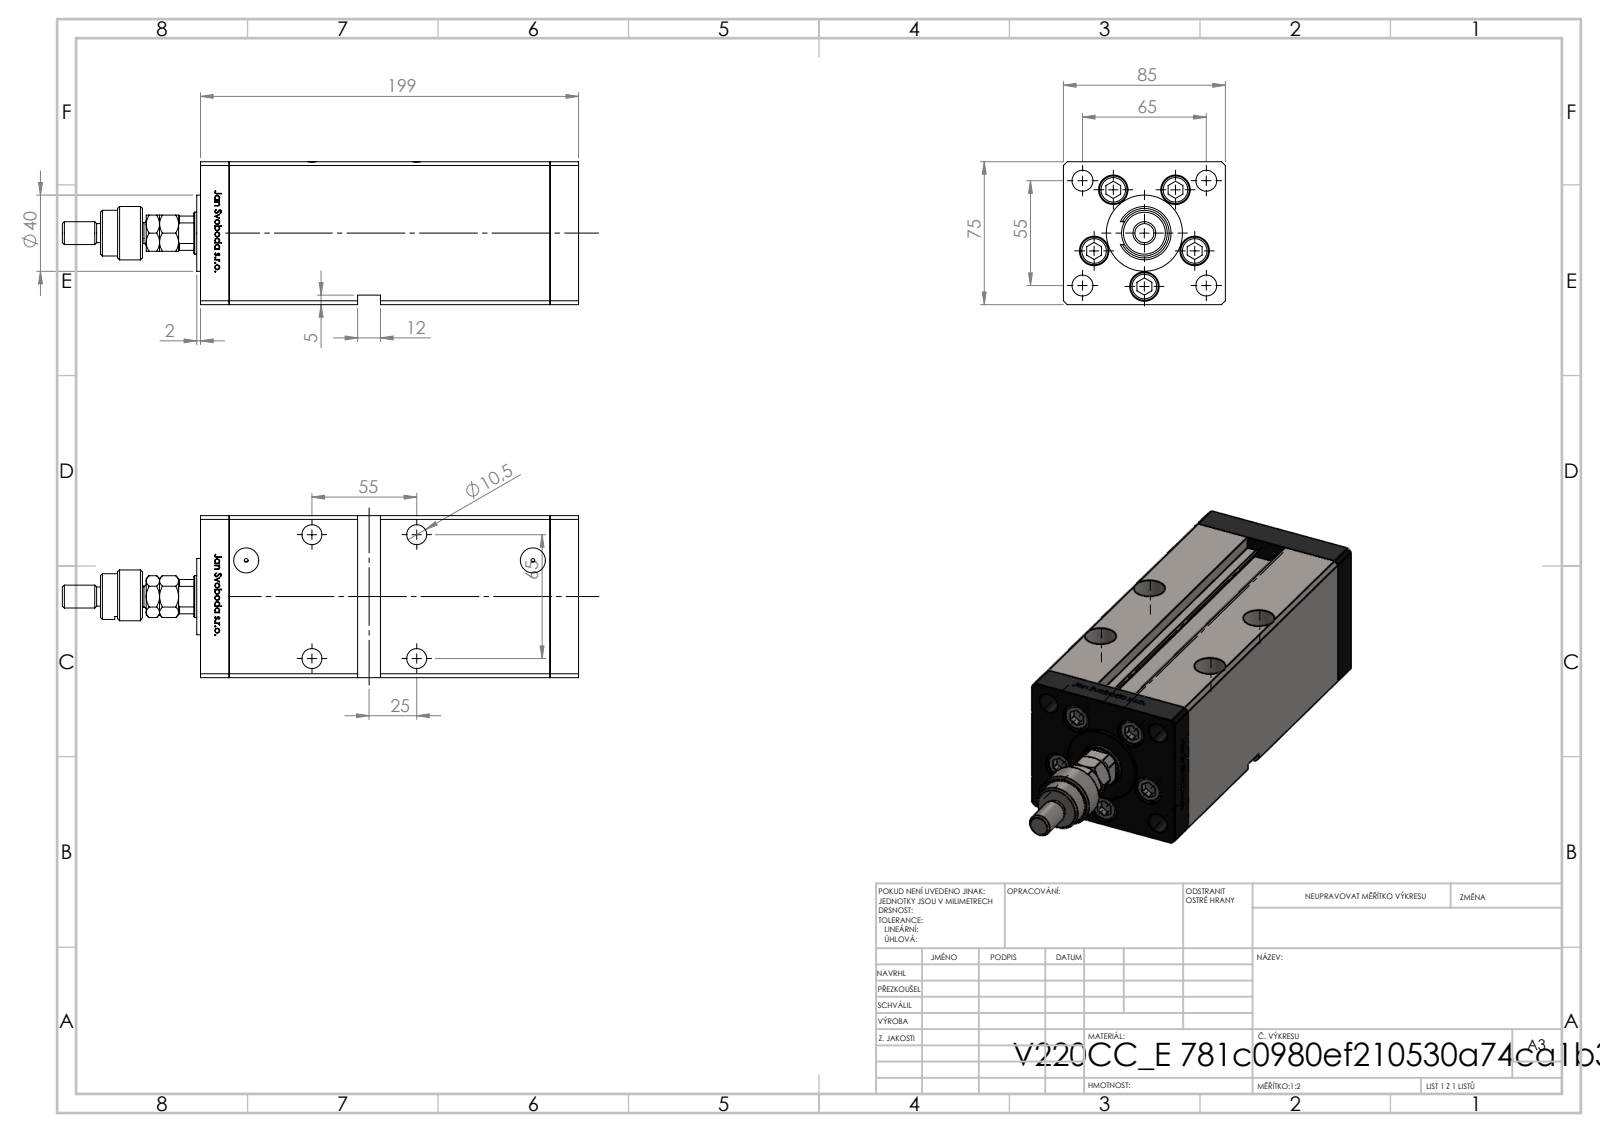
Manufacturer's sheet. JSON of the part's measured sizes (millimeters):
{"part_name": "FEMALE_PART_FOR_DFA; V220C_FRONT_E; V220C_E MIDDLE; ALLEN BOLT (+3 more)", "step_written_by": "SolidWorks 2019 (CONFIG_CONTROL_DESIGN)", "units": "millimeters", "bodies": {"solids": 16, "faces": 1299, "planar": 503, "cylindrical": 178, "other": 618}, "overall_size": [271, 85, 75], "volume_mm3": 1094000, "surface_area_mm2": 189973, "round_holes": [[11, 9], [15.5, 5], [10.5, 4], [16.5, 4], [2, 2], [13.16, 2], [13.5, 1], [22, 1], [23.5, 1]], "round_bosses_or_shafts": [[14.5, 5], [8, 5], [40, 1], [28, 1], [24, 1], [18, 1], [12, 1], [11, 1]], "partial_cylinders_radius": [[0.93, 2], [9.75, 1], [10.5, 1]], "face_to_face_distances": [85, 75, 15, 168.5, 183.5, 198.5, 34.25, 10.5, 64.5, 68.5], "hole_center_spacings": [28, 42.57, 55, 65, 85.15, 16.86, 19.17, 32.33]}
